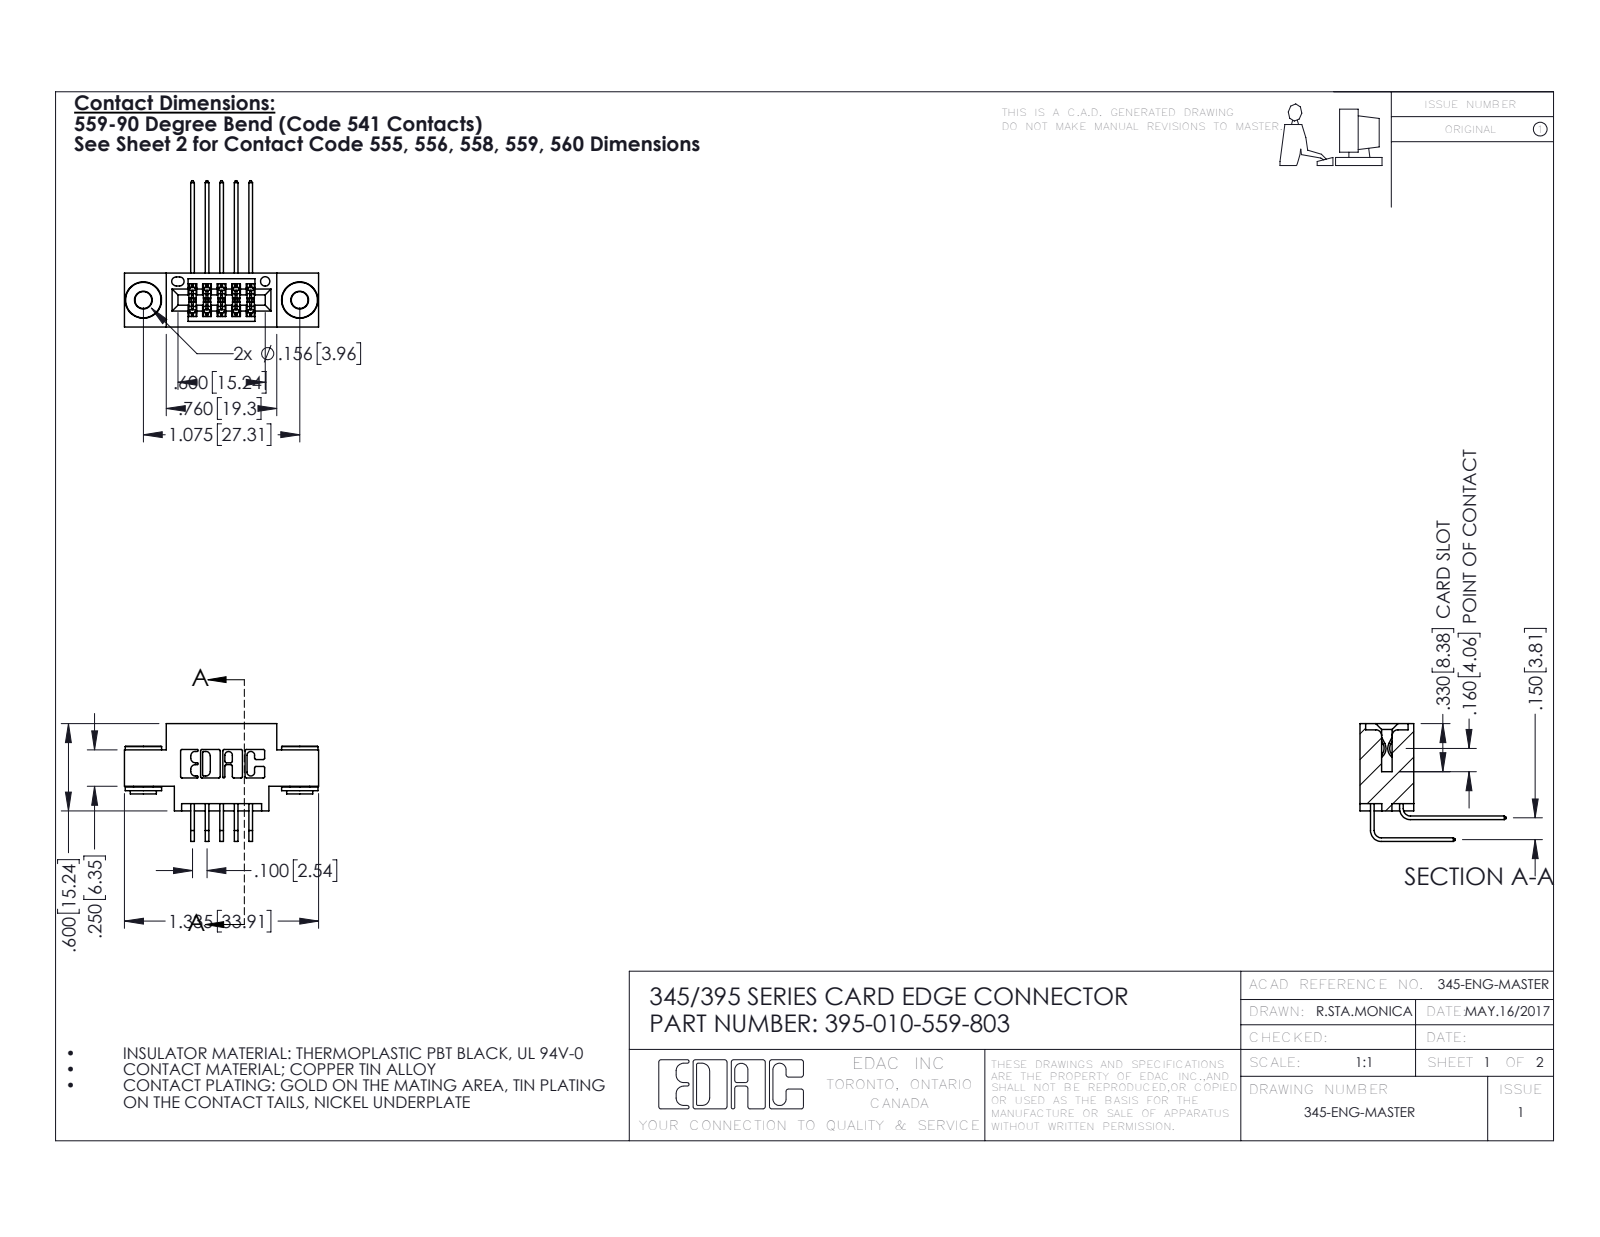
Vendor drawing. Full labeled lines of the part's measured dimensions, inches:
Part name (STEP PRODUCT): 395-010-559-803; 345-250-002_345-250-002-102; 345 Part_0.170 Offset - 0.156 Dia-TH; 345-292-001_559 Tail - 2 (+1 more)
STEP written by: SolidWorks 2016 (CONFIG_CONTROL_DESIGN)
Units: inches
Bodies: 13 solids, 688 faces (444 planar, 236 cylindrical, 8 other)
Overall size (bounding box): 1.335 × 1.005 × 0.809
Volume: 0.178 in³ · Surface area: 6.527 in²
Round holes (diameter × count): ⌀0.116 ×2, ⌀0.156 ×2, ⌀0.064 ×1
Round bosses / shafts (diameter × count): ⌀0.25 ×2, ⌀0.18 ×2, ⌀0.136 ×2
Partial cylindrical surfaces — rounded edges, fillets, slot ends (radius × count): R0.01 ×22, R0.006 ×16, R0.007 ×6, R0.031 ×6, R0.026 ×3, R0.014 ×2, R0.019 ×2, R0.022 ×2
Main face-to-face distances: 0.2, 0.37, 0.1, 0.072, 0.298, 0.15, 0.175, 0.25, 0.098, 0.272
Hole centre spacings: 0.27, 0.847, 1.075
